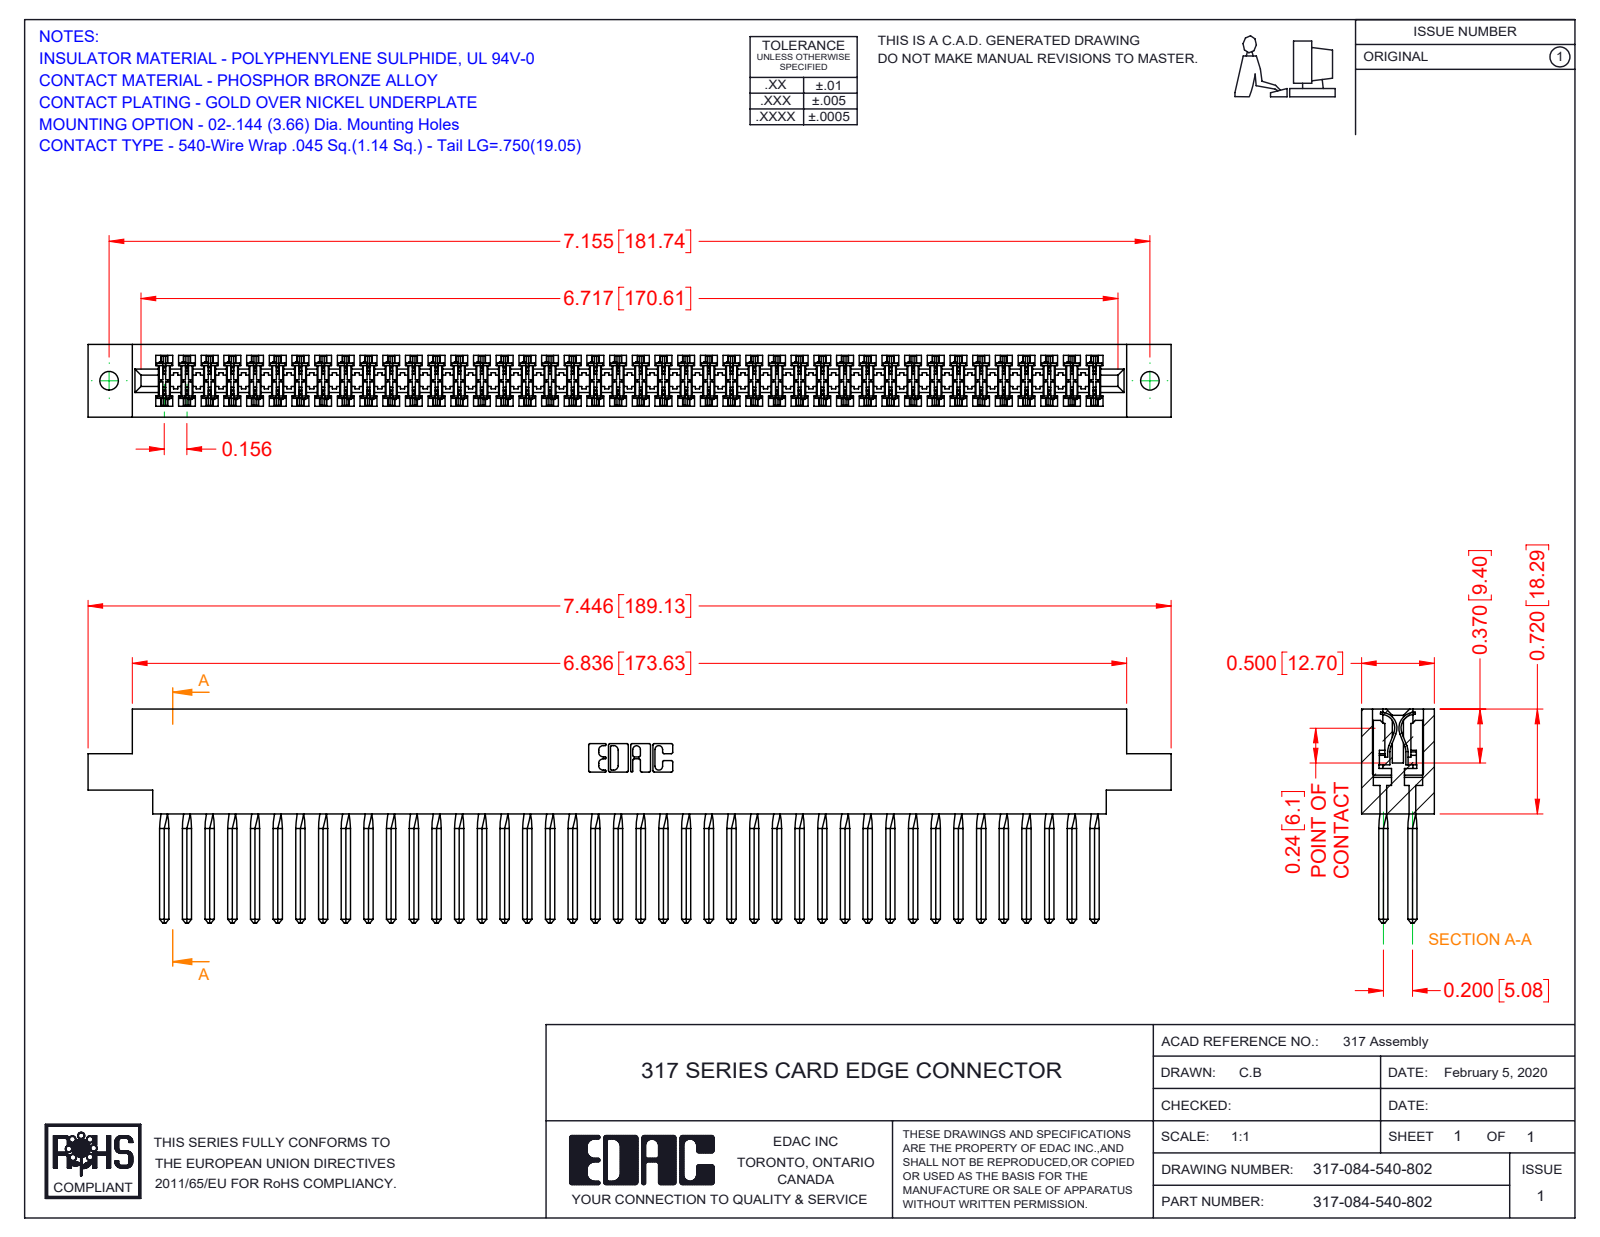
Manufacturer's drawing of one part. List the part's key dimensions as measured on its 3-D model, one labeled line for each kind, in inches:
Part name (STEP PRODUCT): 317 Part_.144 Dia; 317-084-540-802; 317-290-001_540
STEP written by: SolidWorks 2016 (CONFIG_CONTROL_DESIGN)
Units: inches
Bodies: 85 solids, 7578 faces (6190 planar, 1052 cylindrical, 336 other)
Overall size (bounding box): 7.446 × 1.47 × 0.5
Volume: 1.935 in³ · Surface area: 72.86 in²
Round holes (diameter × count): ⌀0.128 ×2
Partial cylindrical surfaces — rounded edges, fillets, slot ends (radius × count): R0.015 ×168, R0.01 ×22, R0.007 ×6, R0.031 ×6, R0.026 ×3, R0.095 ×2, R0.1 ×2, R0.11 ×2
Main face-to-face distances: 0.5, 0.075, 0.425, 0.35, 0.195, 0.094, 0.2, 0.115, 0.131, 0.046
Hole centre spacings: 7.155
